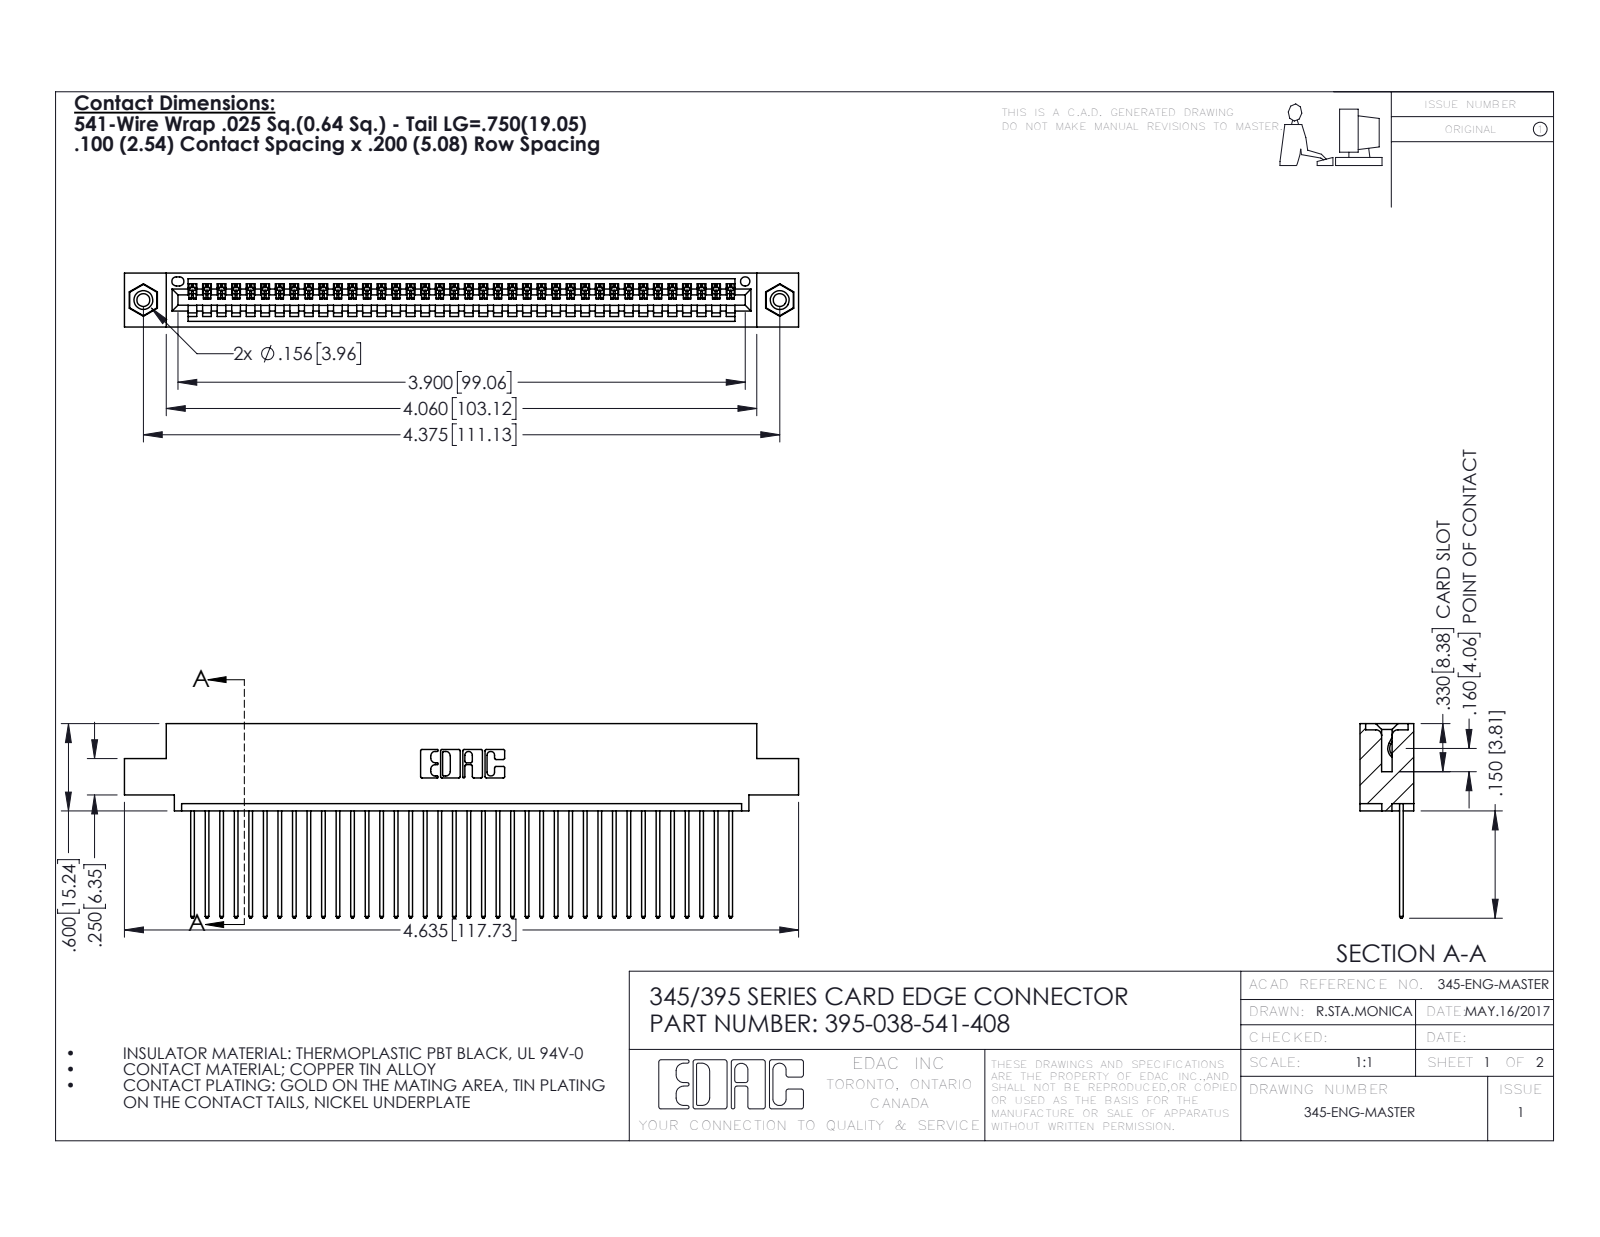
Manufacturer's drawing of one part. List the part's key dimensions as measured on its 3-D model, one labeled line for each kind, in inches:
Part name (STEP PRODUCT): 345-250-001_345-250-003-102; 345 Part_0.110 Offset - 0.156 Dia-TI; 395-038-541-408; 345-292-001_345-293-141
STEP written by: SolidWorks 2016 (CONFIG_CONTROL_DESIGN)
Units: inches
Bodies: 41 solids, 2394 faces (1636 planar, 742 cylindrical, 16 other)
Overall size (bounding box): 4.635 × 1.337 × 0.37
Volume: 0.683 in³ · Surface area: 24.28 in²
Round holes (diameter × count): ⌀0.089 ×2, ⌀0.125 ×2, ⌀0.156 ×2, ⌀0.064 ×1
Round bosses / shafts (diameter × count): ⌀0.155 ×2
Partial cylindrical surfaces — rounded edges, fillets, slot ends (radius × count): R0.006 ×76, R0.01 ×76, R0.01 ×22, R0.007 ×6, R0.031 ×6, R0.026 ×3, R0.031 ×2, R0.04 ×2
Main face-to-face distances: 0.072, 0.298, 0.098, 0.272, 0.025, 0.37, 0.2, 0.225, 0.149, 0.072
Hole centre spacings: 0.27, 4.139, 4.375
